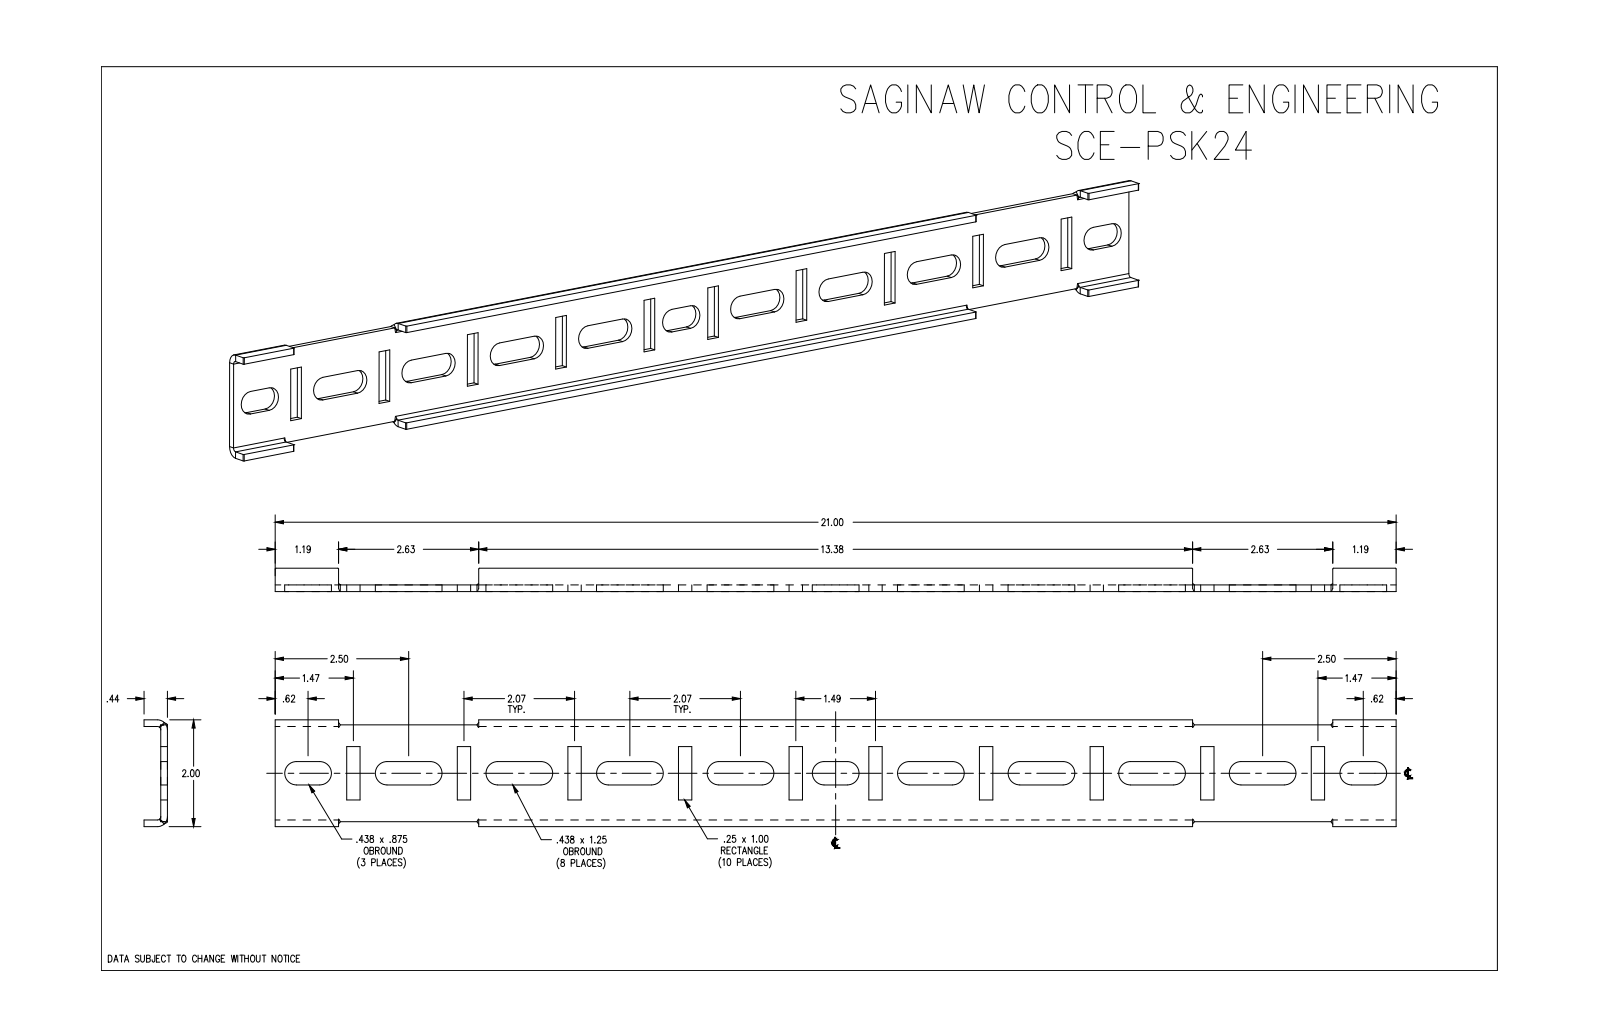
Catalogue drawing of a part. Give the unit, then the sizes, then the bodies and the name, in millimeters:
Units: millimetres
Overall size (bounding box): 577.1 × 533.4 × 406.4
Partial cylindrical surfaces — rounded edges, fillets, slot ends (radius × count): R5.6 ×44, R0.4 ×12, R1.6 ×4, R1.6 ×4, R4.7 ×4, R4.8 ×4
Main face-to-face distances: 3.2, 558, 554.8, 561.2, 355.6, 3.2, 47.6, 50.8, 358.8, 403.2
Volume: 340 900 mm³ · Surface area: 248 800 mm²
Bodies: 4 solids, 664 faces (384 planar, 184 cylindrical, 96 other)
Part name (STEP PRODUCT): SCE-PSK24
STEP written by: SolidWorks 2019 (CONFIG_CONTROL_DESIGN)
